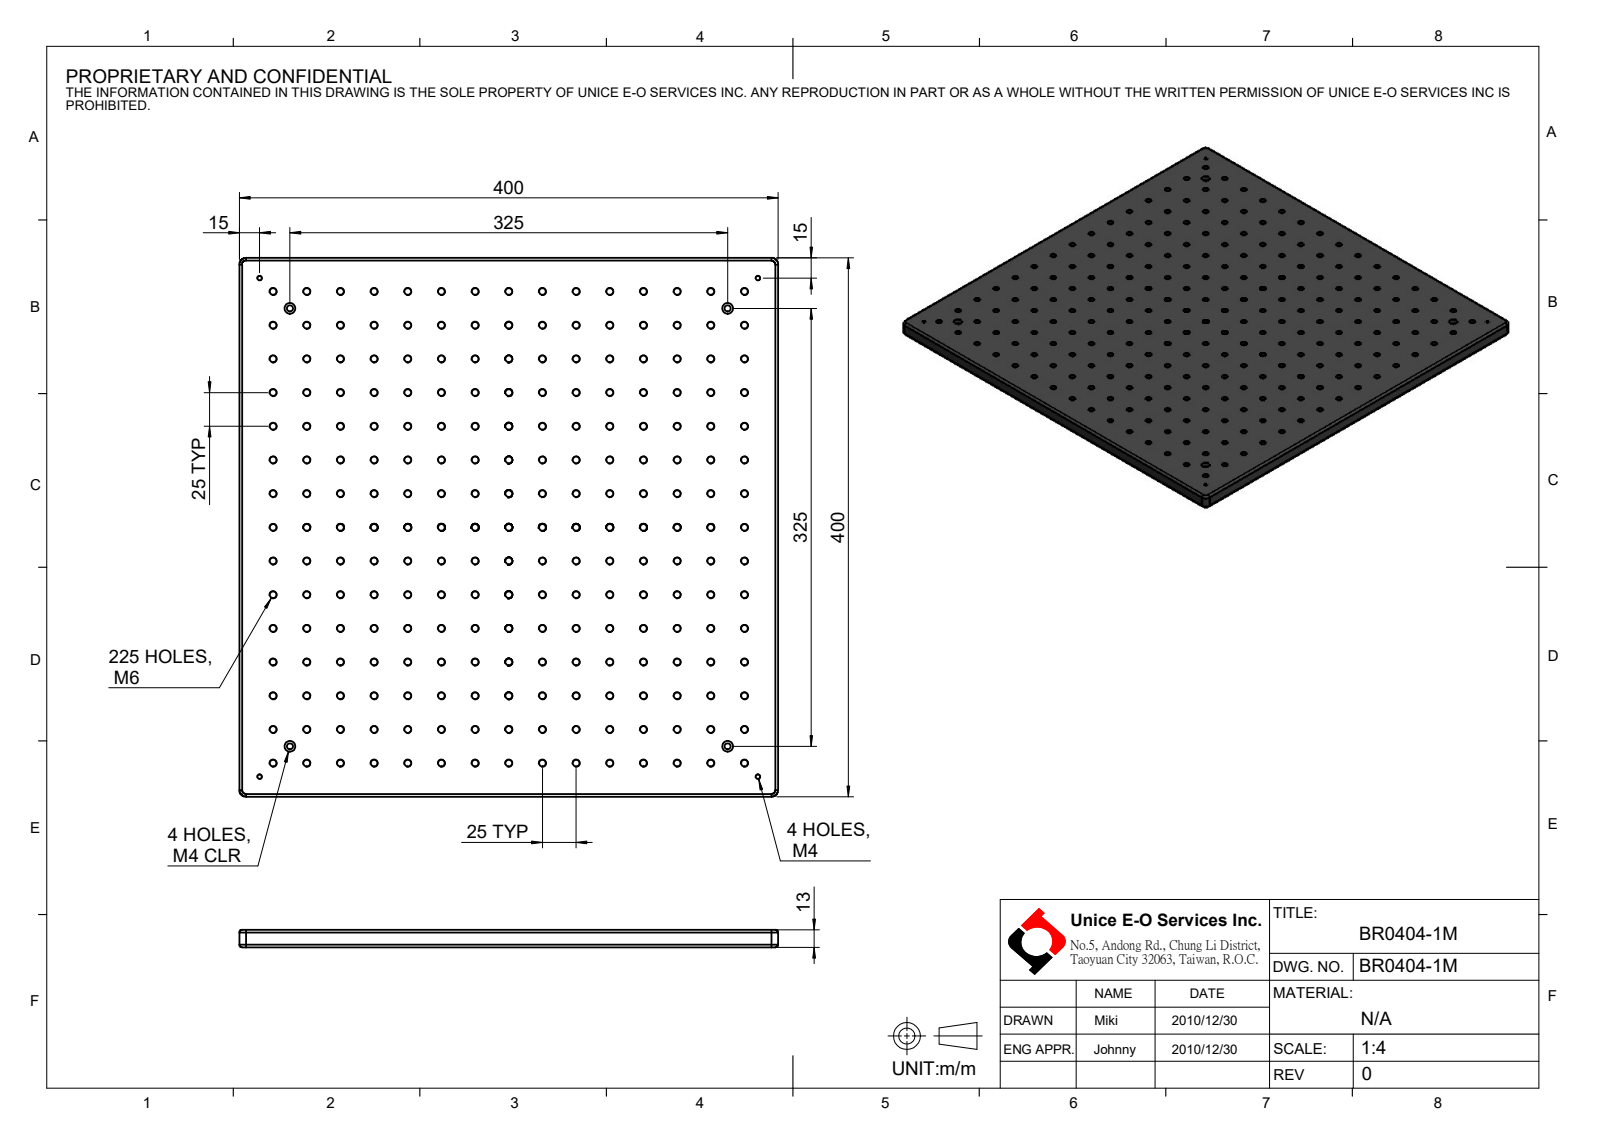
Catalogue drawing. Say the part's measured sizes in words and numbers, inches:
The part is named "BR0404-1M". Its 3-D file was written by "SolidWorks 2016 (CONFIG_CONTROL_DESIGN)". It is 1 solid with 504 faces: 10 planar, 486 cylindrical and 8 other. Overall it measures 15.748 by 15.748 by 0.512 inches. Its volume is 123.1 cubic inches and its surface area 583.2 square inches. Round holes: 225 of diameter 0.197, 4 of diameter 0.13, 4 of diameter 0.177, 4 of diameter 0.315. Partial cylindrical surfaces (rounded edges, fillets, slot ends): 8 of radius 0.079, 4 of radius 0.197. The main face-to-face distances are 0.512, 15.748, 0.354, 0.157. The hole center spacings are 0.984, 1.392, 2.201, 1.969, 3.113, 2.953, 4.058, 3.937.
